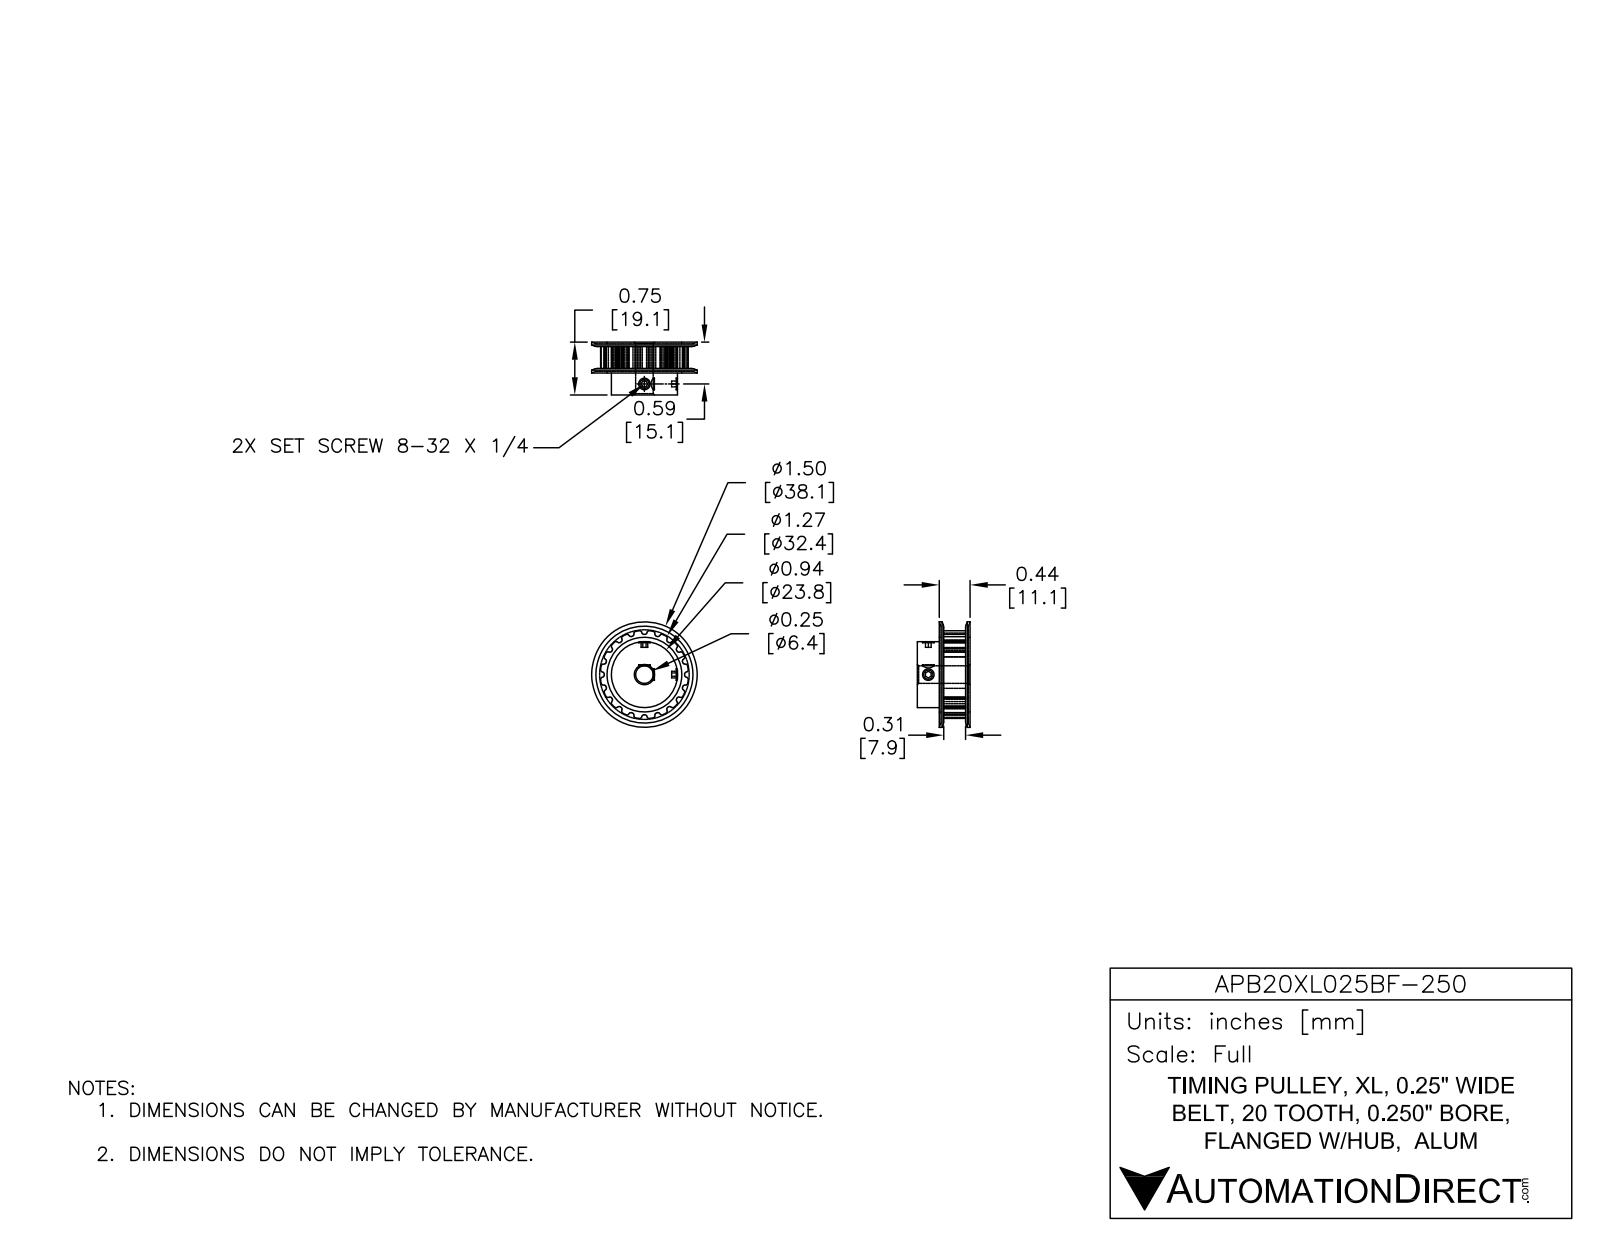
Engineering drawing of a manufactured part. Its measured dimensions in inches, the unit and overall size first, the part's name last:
Units: inches
Overall size (bounding box): 1.5 × 1.5 × 0.75
Round holes (diameter × count): ⌀0.088 ×2, ⌀0.25 ×1
Round bosses / shafts (diameter × count): ⌀0.938 ×1
Partial cylindrical surfaces — rounded edges, fillets, slot ends (radius × count): R0.015 ×80, R0.571 ×1
Main face-to-face distances: 0.343, 0.033, 0.375, 0.75, 0.407, 0.717, 1.253, 0.437, 0.065, 0.032
Volume: 0.689 in³ · Surface area: 8.367 in²
Bodies: 1 solid, 215 faces (66 planar, 127 cylindrical, 22 other)
Part name (STEP PRODUCT): APB20XL025BF-250
STEP written by: SolidWorks 2014 (AUTOMOTIVE_DESIGN)
